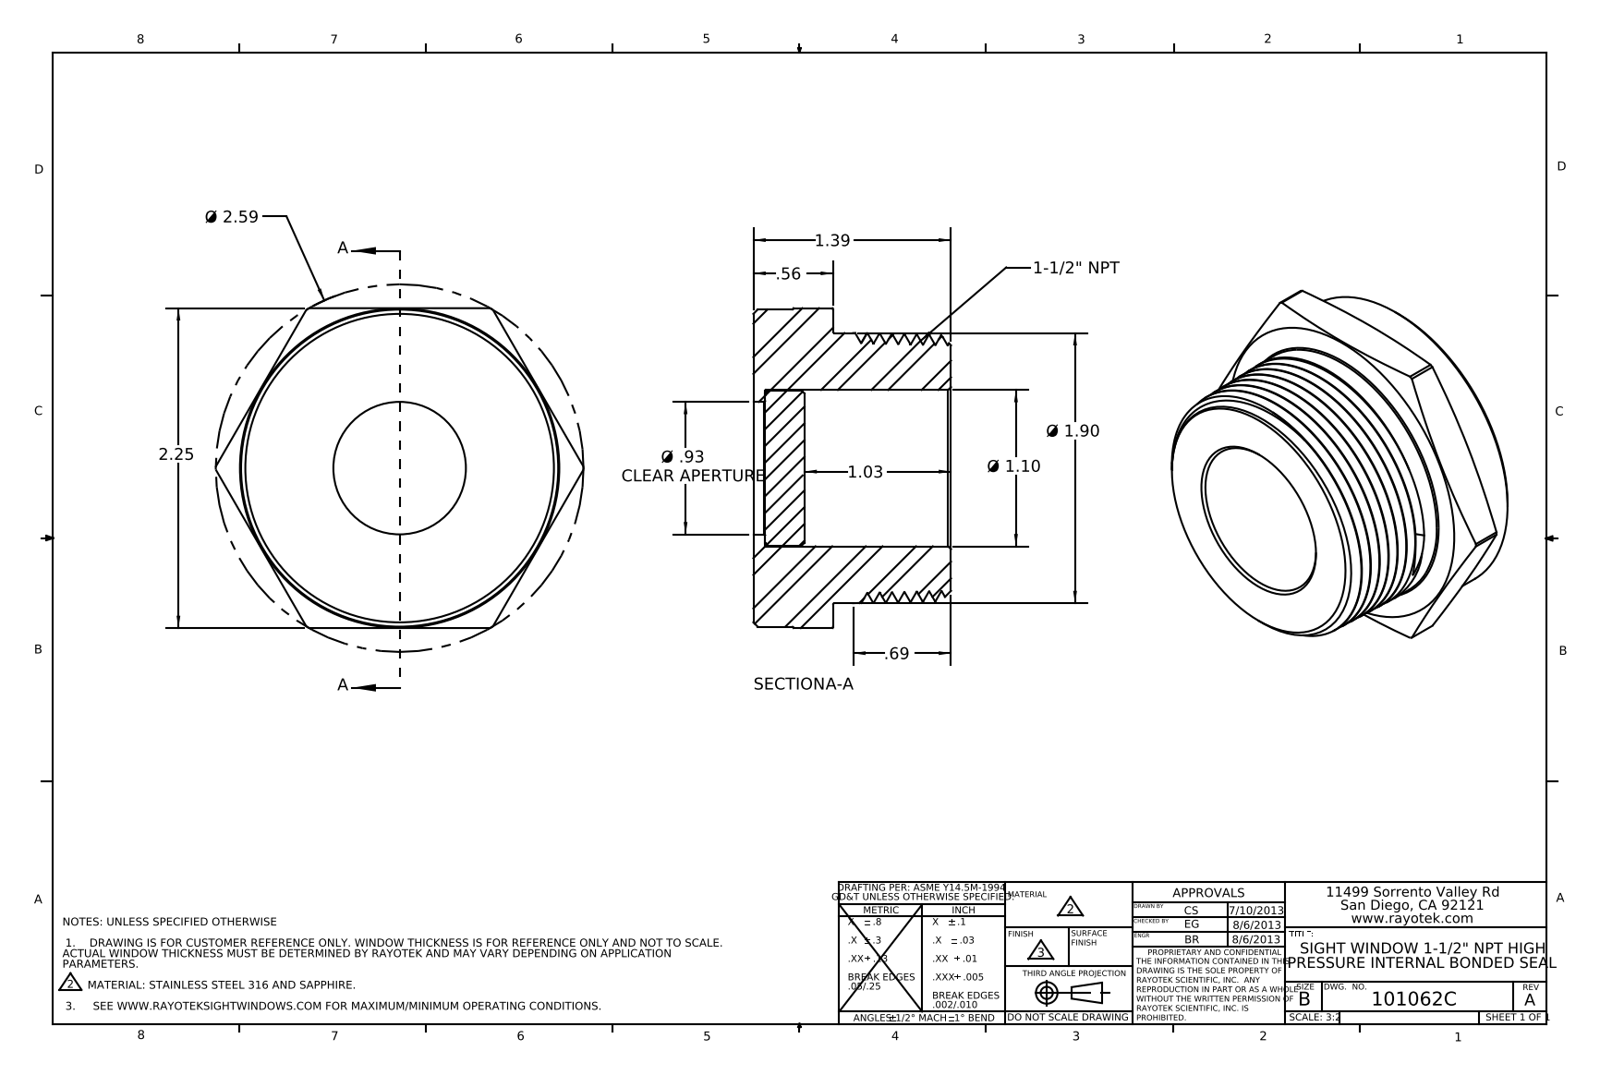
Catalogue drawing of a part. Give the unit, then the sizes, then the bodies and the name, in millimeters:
Units: millimetres
Overall size (bounding box): 65.7 × 58.1 × 57.2
Round holes (diameter × count): ⌀23.7 ×1, ⌀27.9 ×1
Round bosses / shafts (diameter × count): ⌀56.6 ×1, ⌀48.3 ×1, ⌀27.7 ×1
Partial cylindrical surfaces — rounded edges, fillets, slot ends (radius × count): R32.8 ×1
Main face-to-face distances: 35.3, 14.2, 21.1, 57.2, 58.1, 43.9, 22.8, 51.1, 36.9, 15.8
Volume: 56 540 mm³ · Surface area: 16 880 mm²
Bodies: 2 solids, 73 faces (15 planar, 17 cylindrical, 41 other)
Part name (STEP PRODUCT): 101062; 500365; 402062; 403062
STEP written by: SolidWorks 2012 (AUTOMOTIVE_DESIGN)
